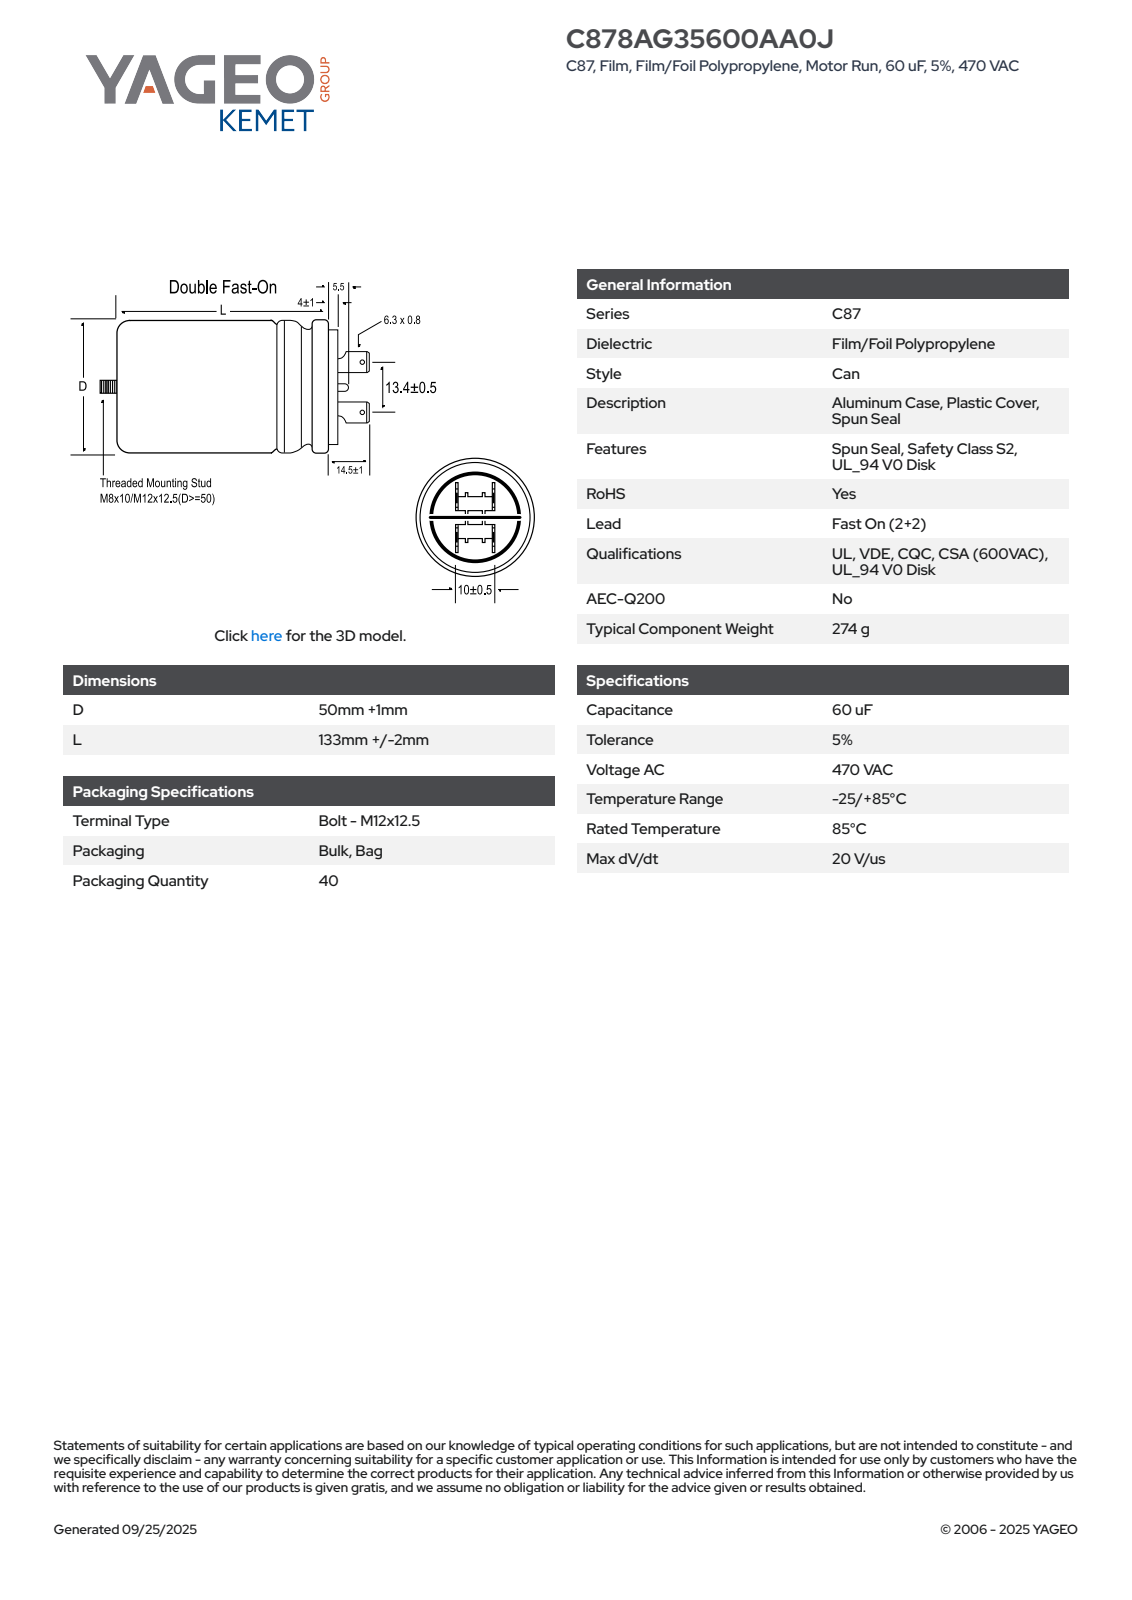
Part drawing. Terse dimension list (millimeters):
name: CFM_C87DF_50X133_D51L135
written by: SolidWorks 2021 (AUTOMOTIVE_DESIGN)
unit: mm
bodies: 1 solid, 153 faces (52 planar, 58 cylindrical, 43 other)
size: 163 × 51 × 51
volume: 278 279 mm³; area: 27 734 mm²
holes: 2× ⌀1.2
bosses: 1× ⌀51, 1× ⌀43.54, 1× ⌀12
rounds: 9× R0.25, 2× R4, 1× R25.49
face distances: 140, 126.5, 13.5, 135, 8.5, 5, 0.8, 9.7, 107.86, 18.64
hole spacings: 13.9
